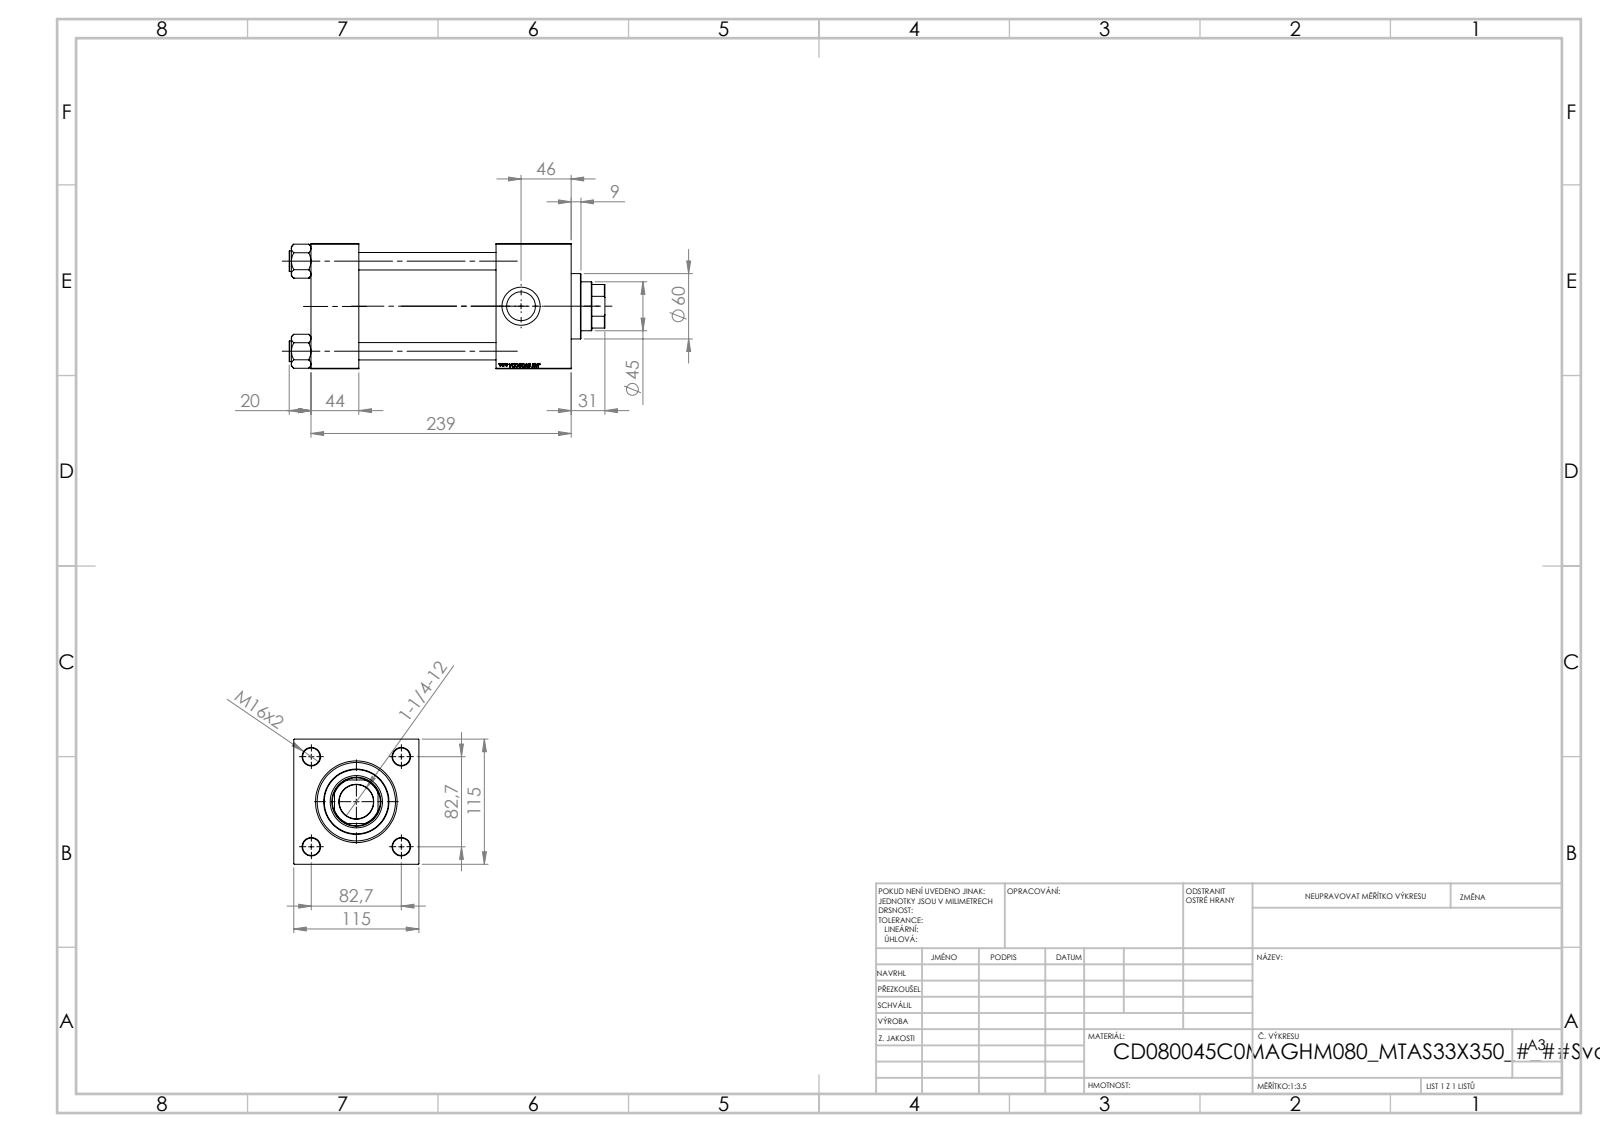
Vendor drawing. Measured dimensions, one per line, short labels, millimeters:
name: V215CD_C_TYCINKA; NUT_M5_V215CD_C; V215CD_Body_C; V215CD_VC_C (+1 more)
written by: SolidWorks 2019 (CONFIG_CONTROL_DESIGN)
unit: mm
bodies: 11 solids, 1197 faces (574 planar, 87 cylindrical, 536 other)
size: 290 × 115 × 115
volume: 2 010 000 mm³; area: 325 721 mm²
holes: 4× ⌀16, 2× ⌀7, 2× ⌀26.44, 2× ⌀35, 1× ⌀31.5, 1× ⌀45, 1× ⌀48, 1× ⌀61, 1× ⌀72, 1× ⌀80
bosses: 4× ⌀19, 1× ⌀86, 1× ⌀60
rounds: 1× R22
face distances: 115, 44, 239, 195, 170, 126, 69, 210.3, 166.3, 40.3
hole spacings: 58.48, 82.7, 116.96
